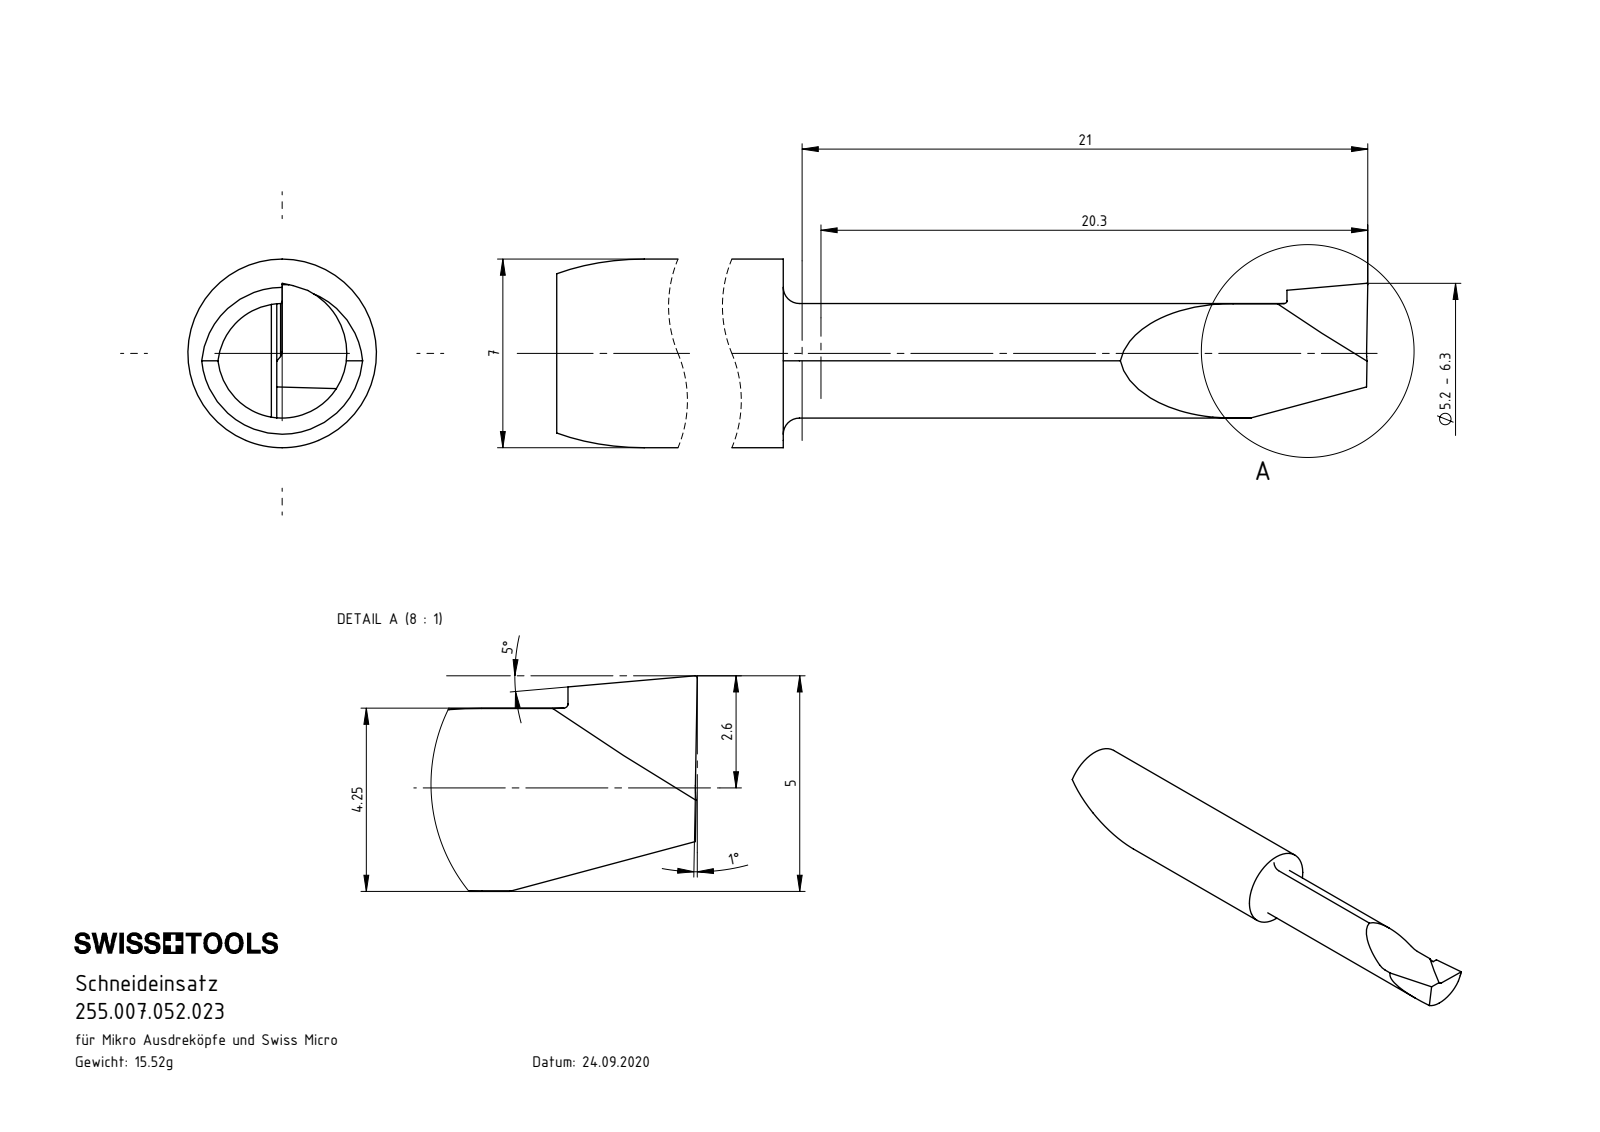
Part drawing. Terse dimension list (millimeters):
name: A07.0245.20.52.05 YR
written by: SolidWorks 2017 (AUTOMOTIVE_DESIGN)
unit: mm
bodies: 1 solid, 27 faces (11 planar, 7 cylindrical, 9 other)
size: 45.5 × 7 × 7
volume: 1 071 mm³; area: 825 mm²
bosses: 1× ⌀7
rounds: 2× R2.4, 1× R1.5, 1× R2.6
face distances: 18.6, 23.8, 18.7, 42.5
